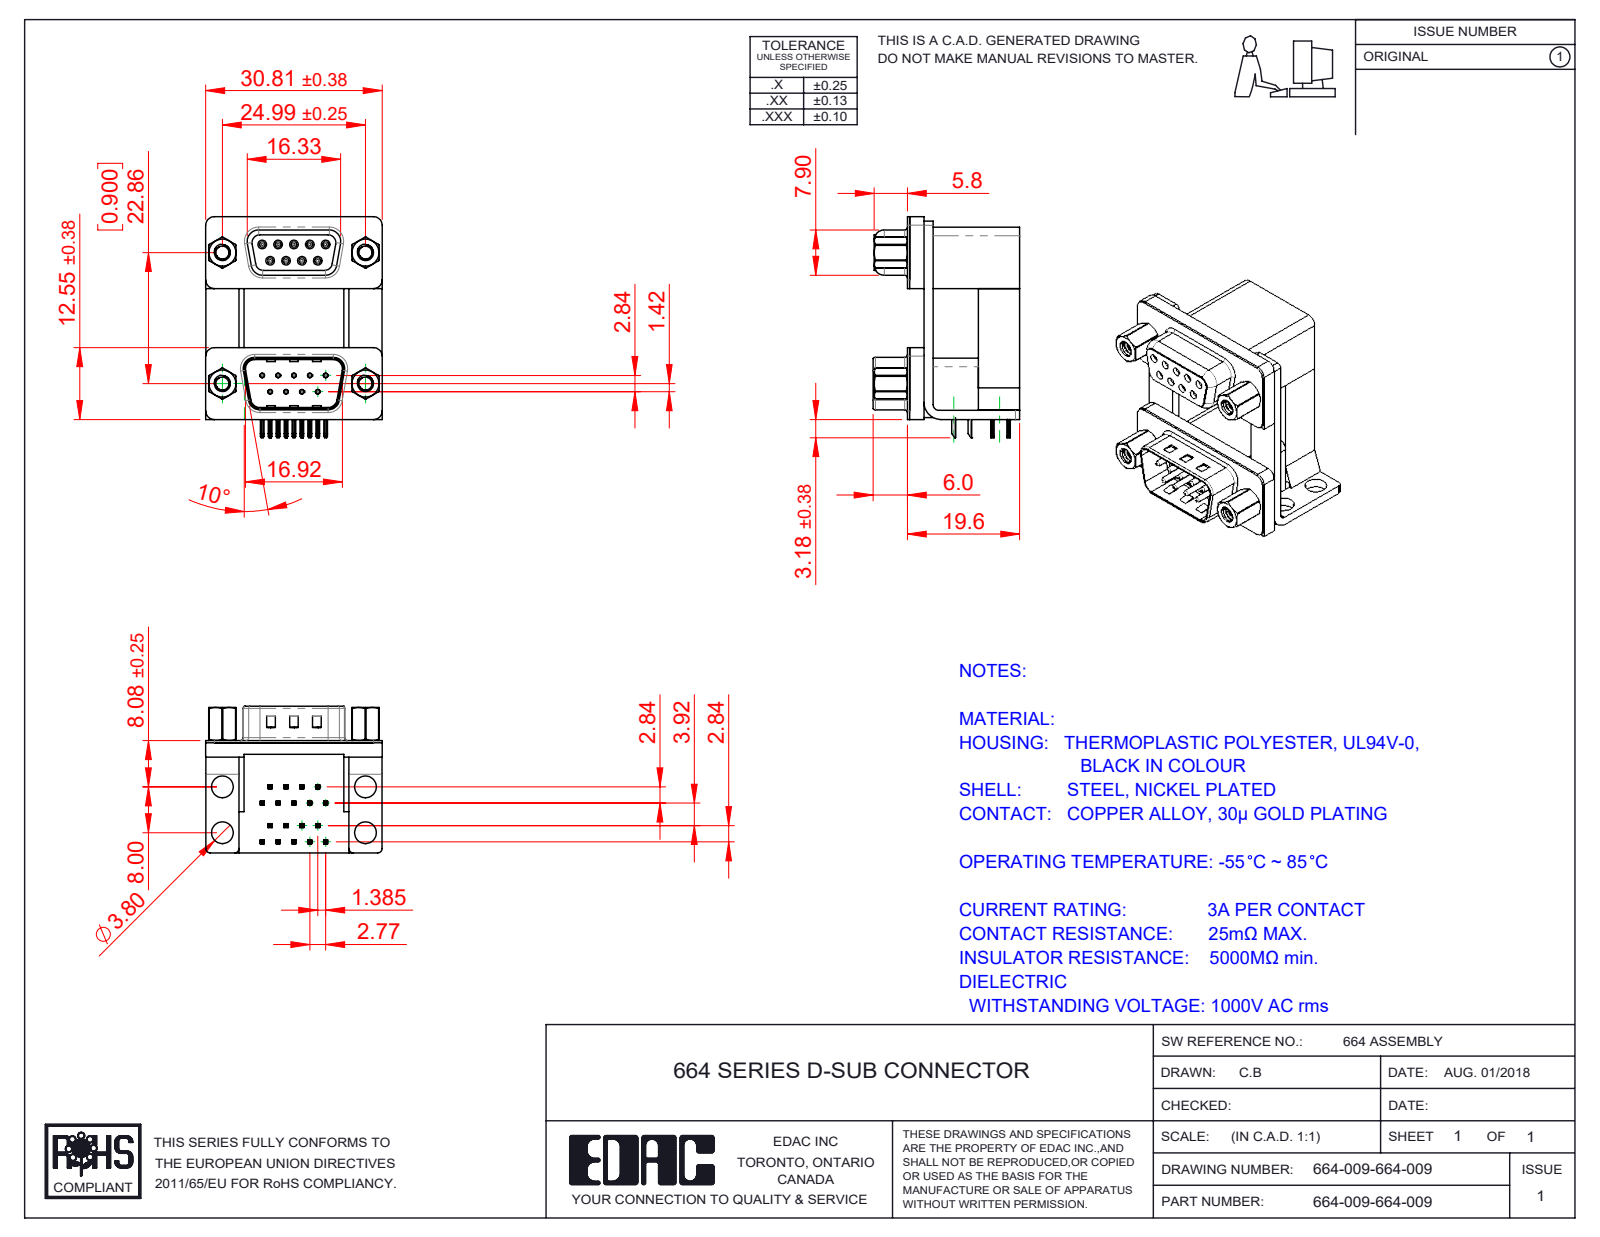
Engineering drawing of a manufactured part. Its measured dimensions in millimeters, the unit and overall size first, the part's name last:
Units: millimetres
Overall size (bounding box): 38.59 × 30.81 × 25.6
Round holes (diameter × count): ⌀0.8 ×18, ⌀0.35 ×9, ⌀0.9 ×9, ⌀2.26 ×4, ⌀2.29 ×4, ⌀3.5 ×4, ⌀3.8 ×4, ⌀4 ×4, ⌀4.8 ×4, ⌀5 ×4
Round bosses / shafts (diameter × count): ⌀1.2 ×9, ⌀0.75 ×9, ⌀4.9 ×4, ⌀4.75 ×4, ⌀3.9 ×4, ⌀2.79 ×4
Partial cylindrical surfaces — rounded edges, fillets, slot ends (radius × count): R0.1 ×72, R0.15 ×36, R0.25 ×36, R0.12 ×18, R0.35 ×18, R1.5 ×13, R0.5 ×12, R0.34 ×9
Main face-to-face distances: 0.4, 2.5, 16.7, 19.2, 12, 7.2, 9.5, 12.4, 1.6, 19.6
Hole centre spacings: 3.16, 23.03, 2.77, 22.86, 23.52, 25.74, 5.54, 26.03
Volume: 11 720 mm³ · Surface area: 13 976 mm²
Bodies: 33 solids, 2781 faces (1307 planar, 839 cylindrical, 635 other)
Part name (STEP PRODUCT): 664 Threaded Rivet_4-40; 664 Contact Bottom Upper_H; 664 Shell Receptacle_09 Contacts; 664 Contact Bottom Lower (+8 more)
STEP written by: SolidWorks 2020 (CONFIG_CONTROL_DESIGN)
